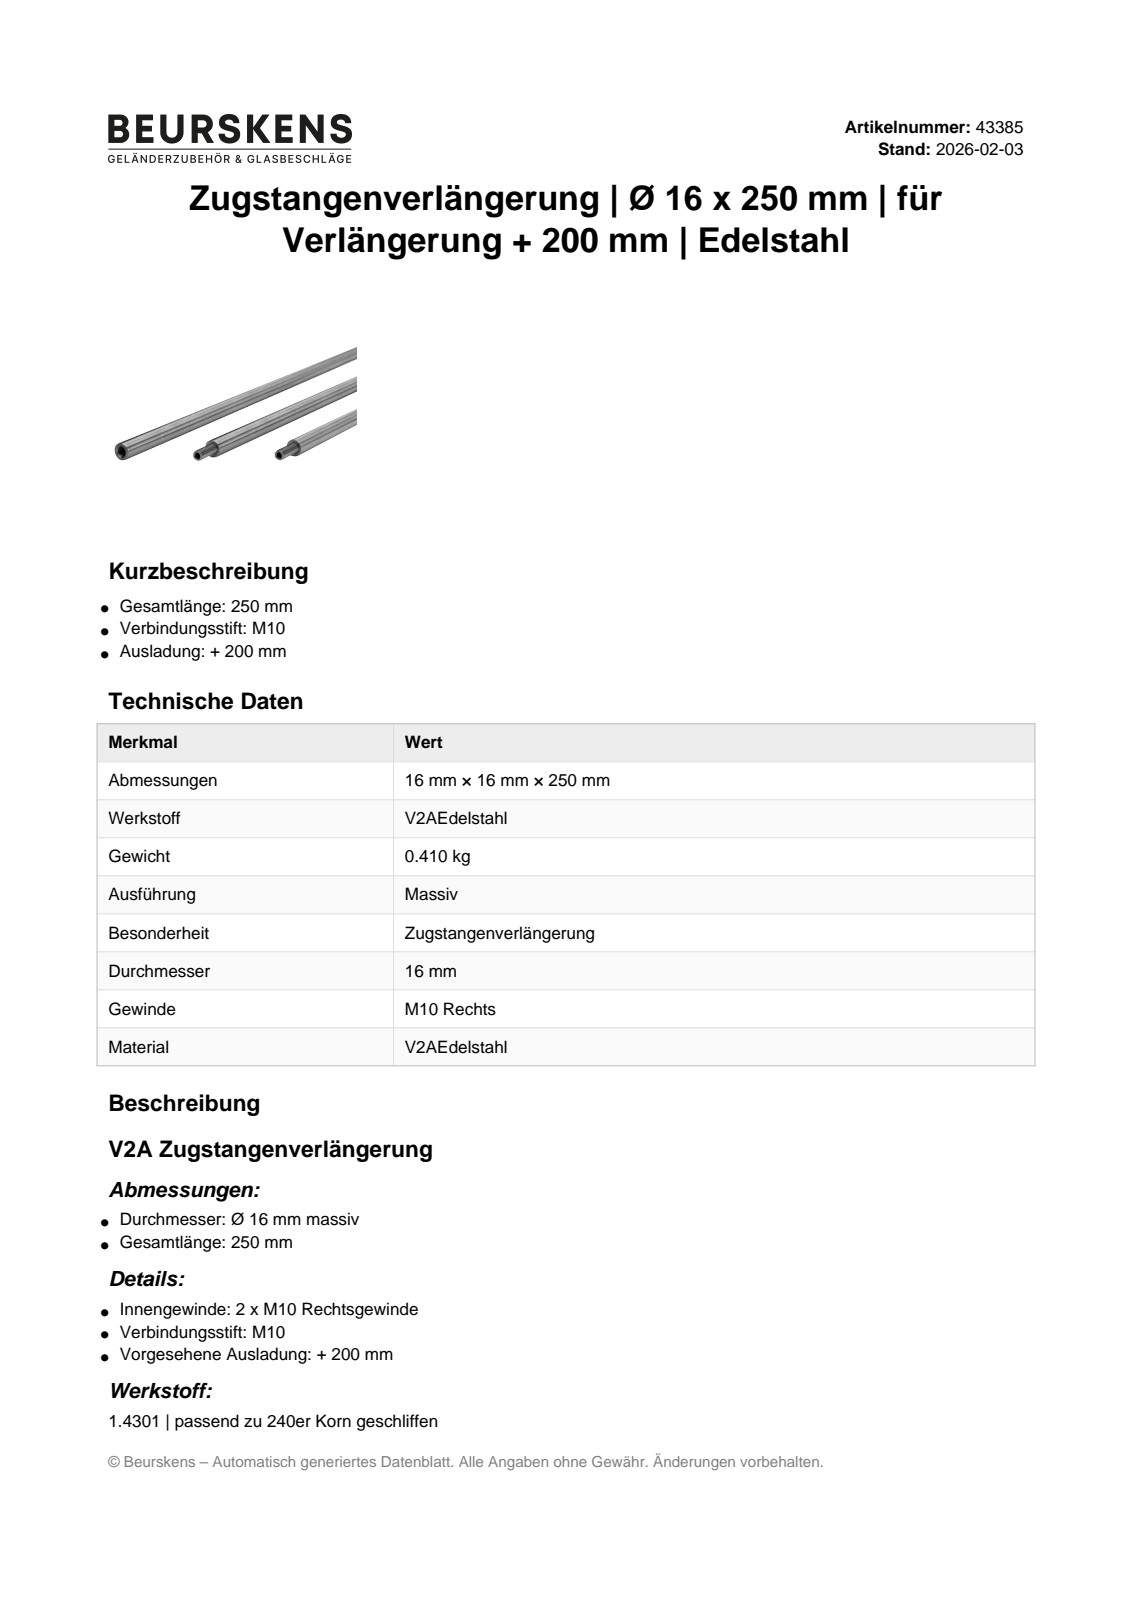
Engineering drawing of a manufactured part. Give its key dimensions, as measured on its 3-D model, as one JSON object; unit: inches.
{"part_name": "43385", "step_written_by": "Autodesk Inventor 2022 (AUTOMOTIVE_DESIGN)", "units": "inches", "bodies": {"solids": 1, "faces": 7, "planar": 4, "cylindrical": 3, "other": 0}, "overall_size": [9.843, 0.63, 0.63], "volume_in3": 2.54, "surface_area_in2": 25.46, "round_holes": [[0.394, 1]], "round_bosses_or_shafts": [[0.63, 1]], "face_to_face_distances": [2.165, 7.677, 9.843, 5.512]}
